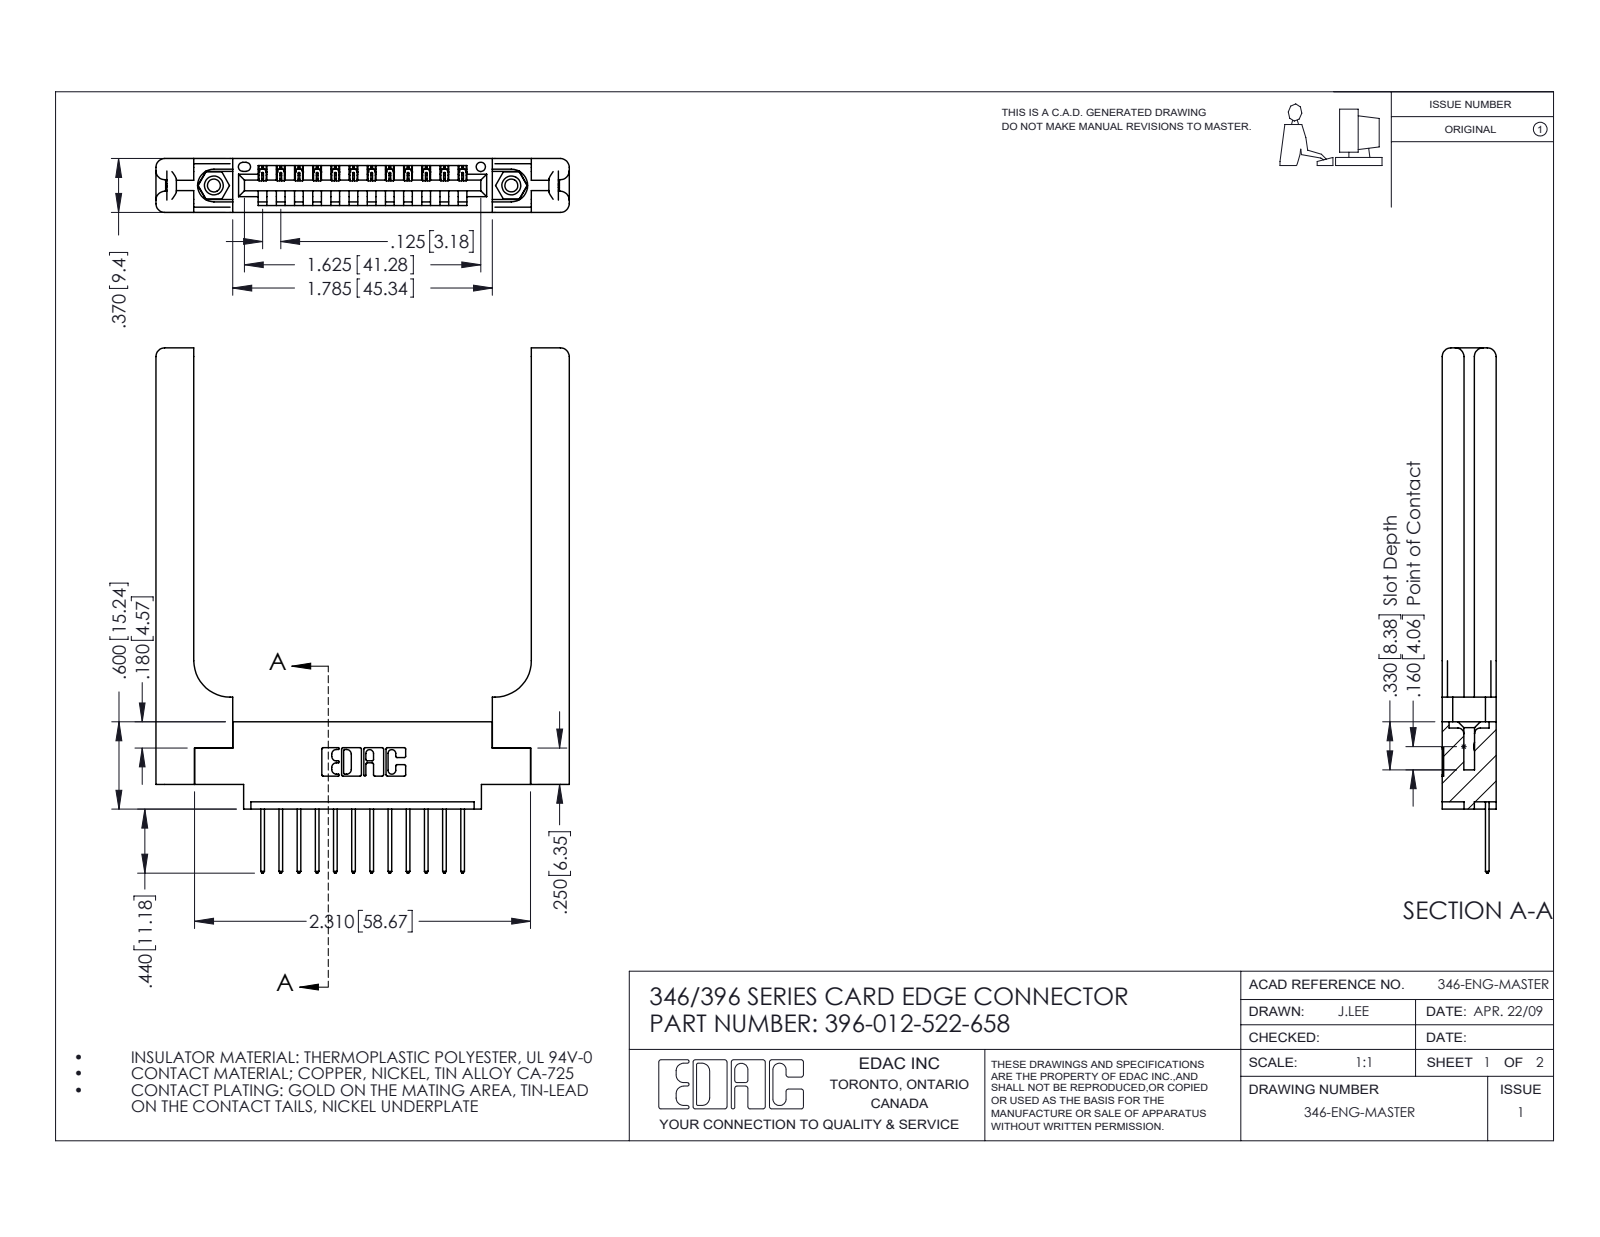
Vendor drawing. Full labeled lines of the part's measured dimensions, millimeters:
Part name (STEP PRODUCT): 396-012-522-658; 345-250-001_345-250-001-102; 346 Part_0.170 Offset - 0.156 Dia-TH; 346-220-058_345-220-058 (+1 more)
STEP written by: SolidWorks 2016 (CONFIG_CONTROL_DESIGN)
Units: millimetres
Bodies: 17 solids, 1078 faces (708 planar, 310 cylindrical, 60 other)
Overall size (bounding box): 91.7 × 72.2 × 9.4
Volume: 14 100 mm³ · Surface area: 13 230 mm²
Round holes (diameter × count): ⌀2.3 ×2, ⌀3.2 ×2, ⌀4 ×2, ⌀1.6 ×1
Round bosses / shafts (diameter × count): ⌀3.9 ×2
Partial cylindrical surfaces — rounded edges, fillets, slot ends (radius × count): R0.2 ×24, R0.3 ×24, R0.3 ×22, R1.5 ×16, R0.2 ×6, R0.8 ×6, R0.7 ×3, R0.8 ×2
Main face-to-face distances: 9.4, 3.8, 1.8, 3.8, 1.2, 8.2, 5.6, 6.4, 2.6, 4.4
Hole centre spacings: 6.2, 46.7, 51.9
